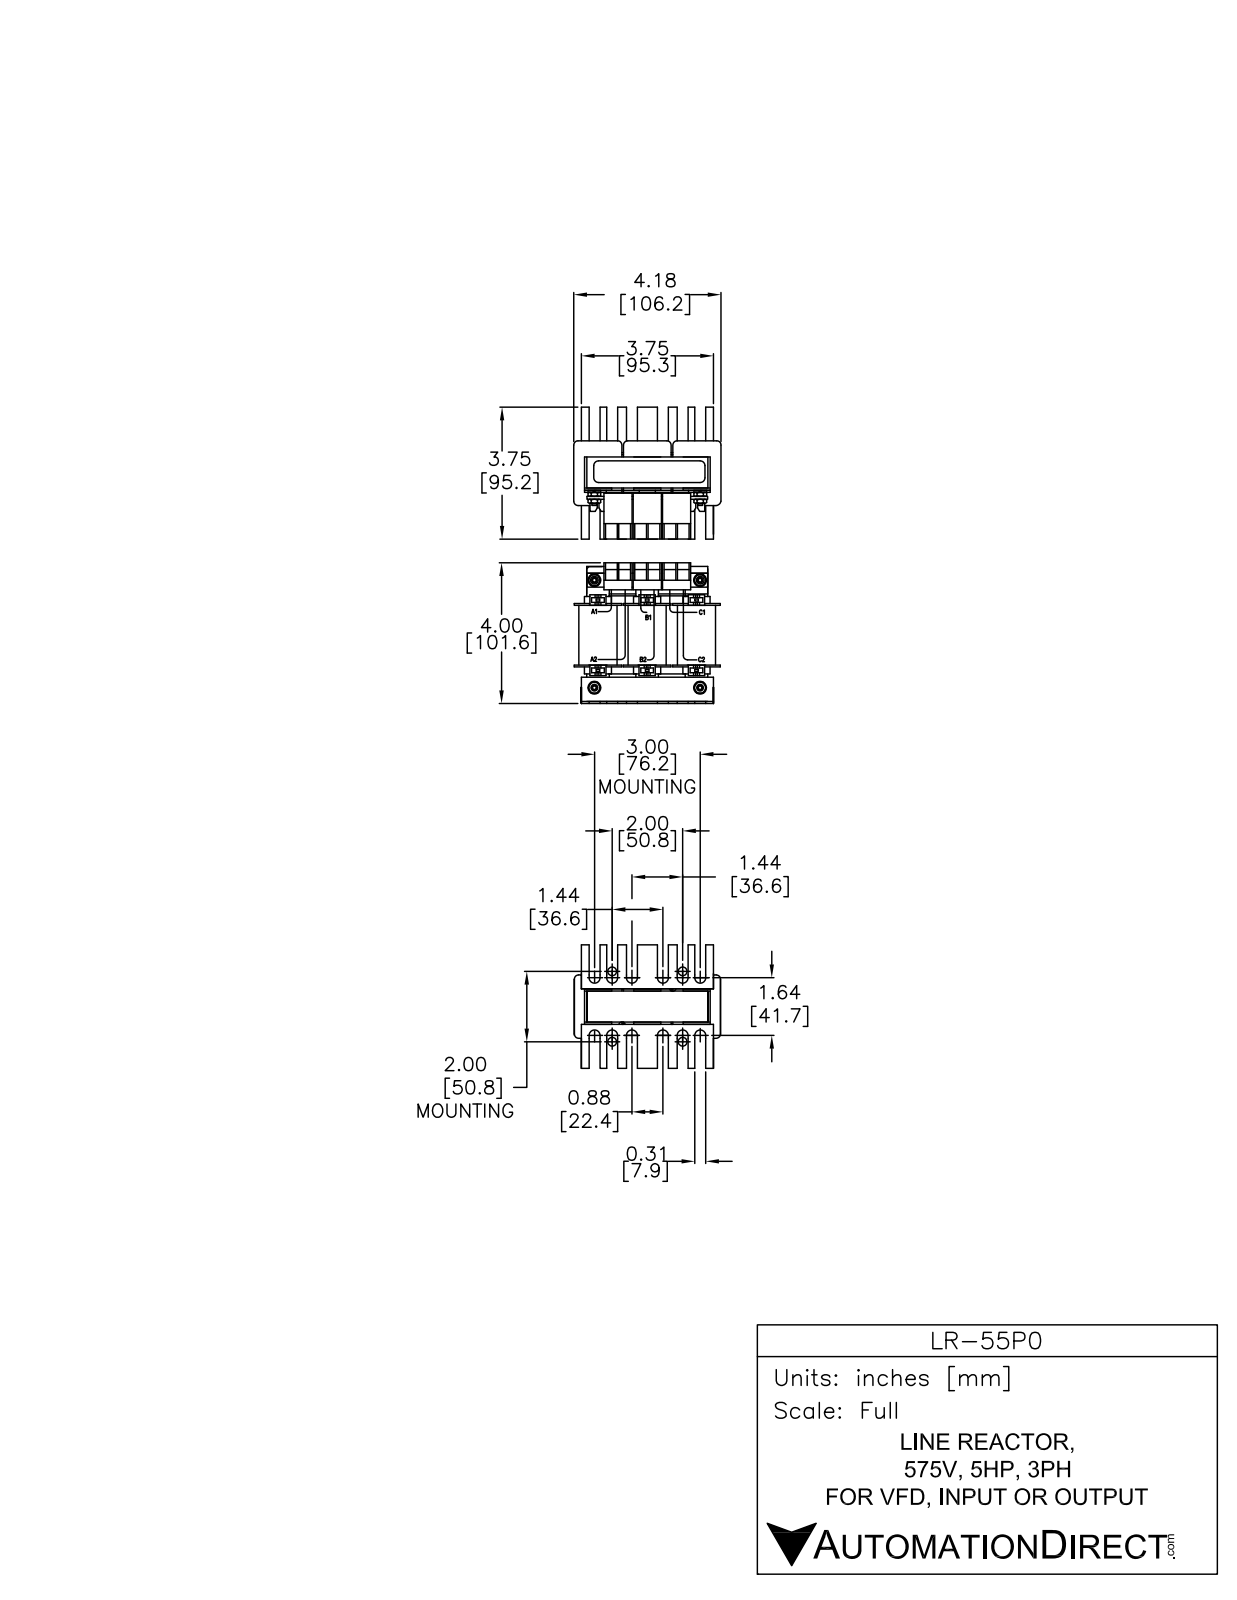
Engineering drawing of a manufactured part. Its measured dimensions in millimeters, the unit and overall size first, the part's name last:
Units: millimetres
Overall size (bounding box): 105.25 × 98.41 × 89.25
Round bosses / shafts (diameter × count): ⌀7.75 ×4, ⌀3.5 ×4
Partial cylindrical surfaces — rounded edges, fillets, slot ends (radius × count): R4 ×50, R1.82 ×24, R8 ×12, R3 ×6, R0.86 ×3, R1.25 ×2
Main face-to-face distances: 5, 21.5, 2.75, 51, 26.25, 26.5, 7.5, 29, 71, 2.5
Volume: 272 326 mm³ · Surface area: 99 223 mm²
Bodies: 17 solids, 941 faces (743 planar, 198 cylindrical, 0 other)
Part name (STEP PRODUCT): LR-55P0
STEP written by: SolidWorks 2011 (AUTOMOTIVE_DESIGN)
